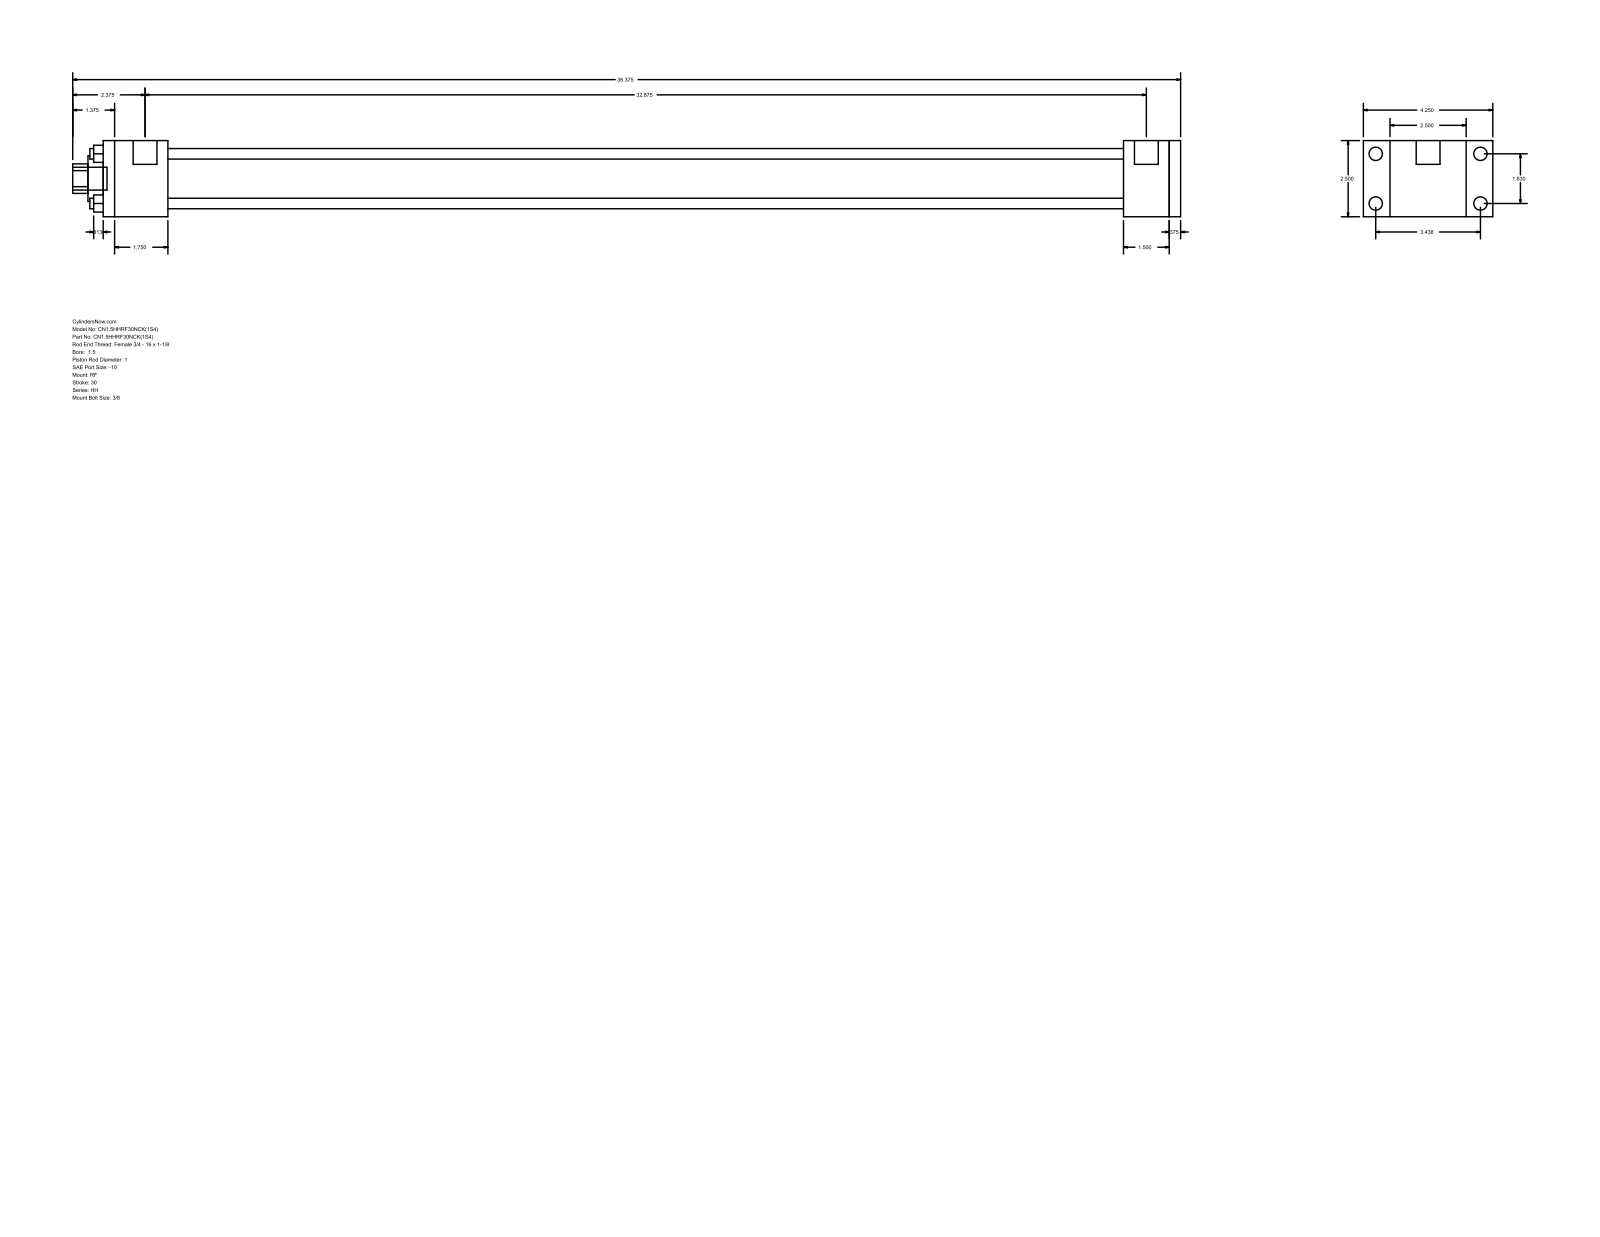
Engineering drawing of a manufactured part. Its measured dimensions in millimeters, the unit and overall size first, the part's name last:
Units: millimetres
Overall size (bounding box): 923.92 × 107.95 × 63.5
Round holes (diameter × count): ⌀8.76 ×4, ⌀25.4 ×1, ⌀38.1 ×1, ⌀44.45 ×1
Round bosses / shafts (diameter × count): ⌀11.13 ×4, ⌀5.56 ×4, ⌀19.84 ×2, ⌀19.05 ×1
Partial cylindrical surfaces — rounded edges, fillets, slot ends (radius × count): R12.29 ×1
Main face-to-face distances: 63.5, 9.52, 796.92, 835.02, 844.54, 38.1, 47.62, 53.98, 850.9, 889
Hole centre spacings: 29.27, 41.4, 58.55
Bodies: 0 solids, 92 faces (64 planar, 28 cylindrical, 0 other)
Part name (STEP PRODUCT): HH_RF__0150_1
STEP written by: GSSL Pune (CONFIG_CONTROL_DESIGN)
